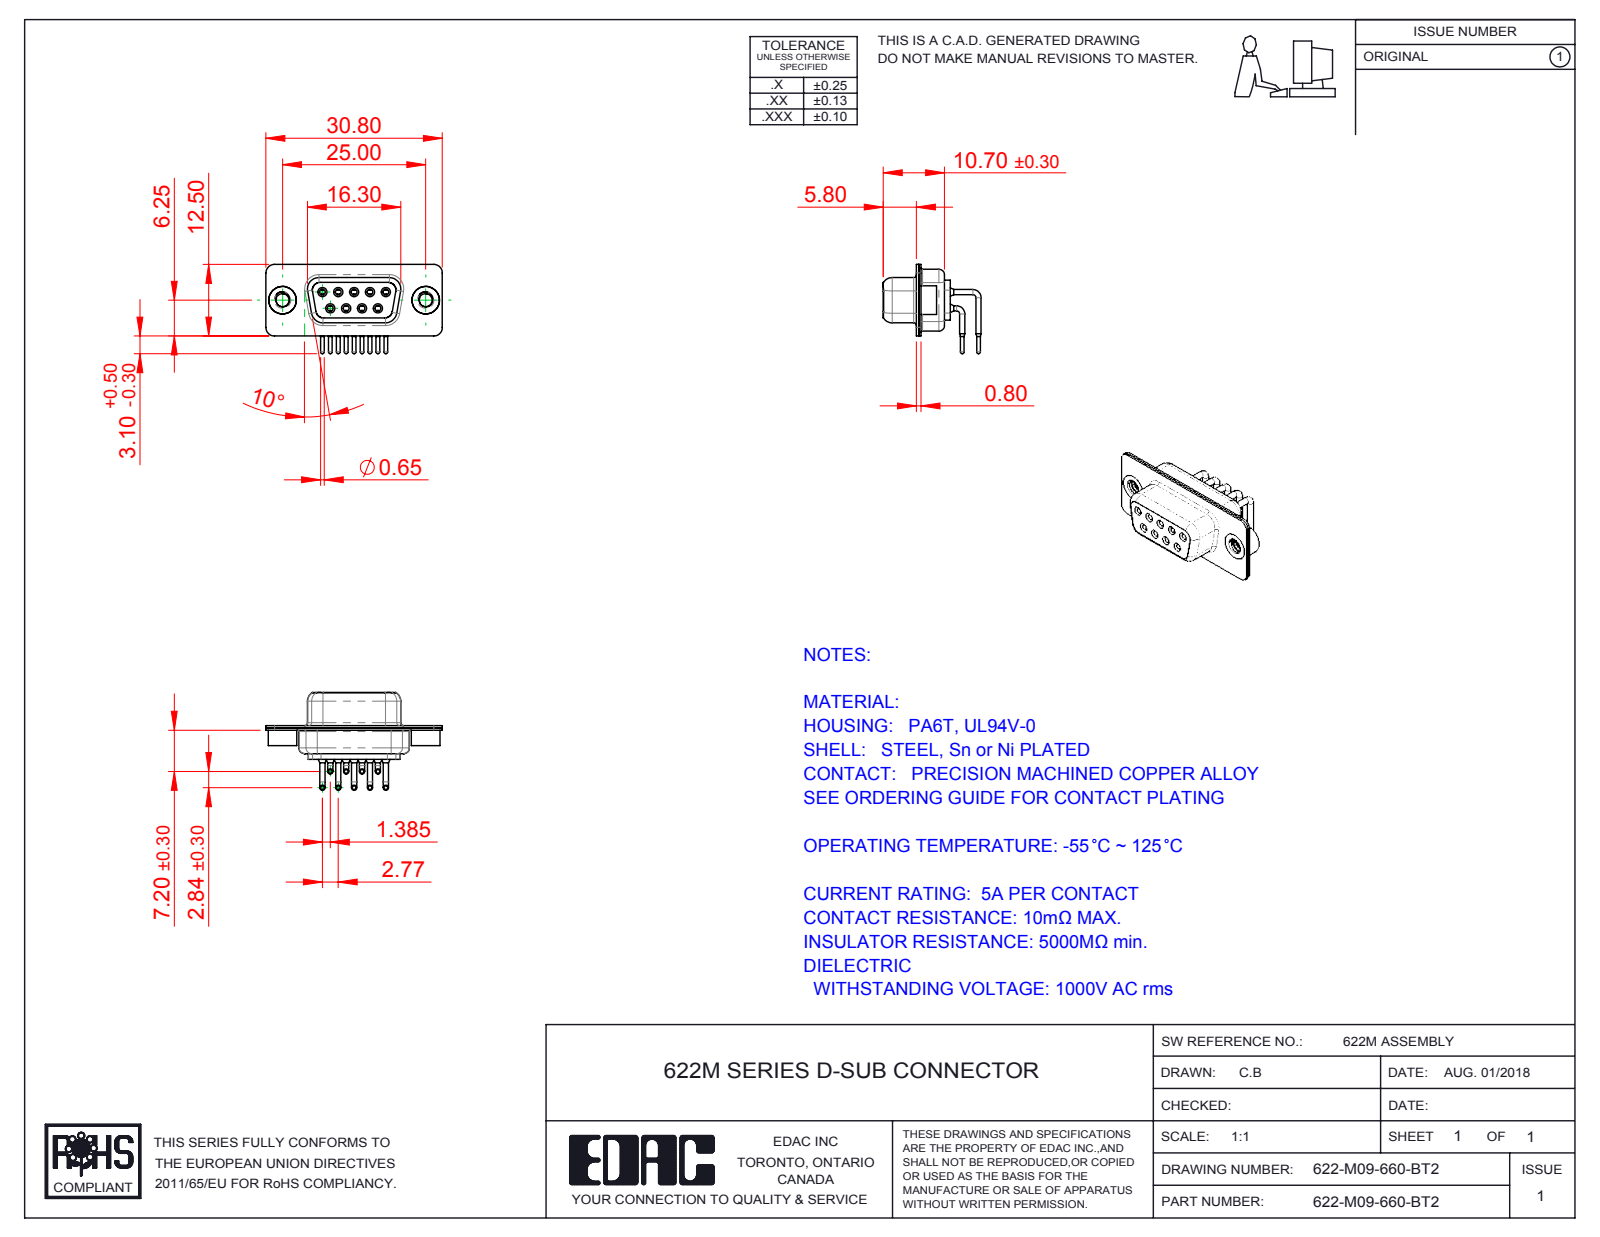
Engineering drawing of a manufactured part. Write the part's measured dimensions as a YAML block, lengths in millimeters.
part_name: "622M 4-40 Threaded Rivet; 622M Housing_09 Contacts; 622-M09-660-BT2; 622M Shell Front_09 Contacts (+3 more)"
step_written_by: "SolidWorks 2016 (CONFIG_CONTROL_DESIGN)"
units: millimeters
bodies: {solids: 14, faces: 756, planar: 202, cylindrical: 344, other: 210}
overall_size: [30.8, 17.09, 15.6]
volume: 1745
surface_area: 4559
round_holes:
  - {diameter: 1, count: 9}
  - {diameter: 1.1, count: 9}
  - {diameter: 1.7, count: 9}
  - {diameter: 1.8, count: 9}
  - {diameter: 2, count: 9}
  - {diameter: 2.26, count: 2}
  - {diameter: 4, count: 2}
  - {diameter: 4.8, count: 2}
round_bosses_or_shafts:
  - {diameter: 0.9, count: 18}
  - {diameter: 1.6, count: 9}
  - {diameter: 1.5, count: 9}
  - {diameter: 0.65, count: 9}
  - {diameter: 5, count: 2}
  - {diameter: 4.9, count: 2}
partial_cylinders:
  - {radius: 1.5, count: 16}
  - {radius: 2, count: 12}
  - {radius: 1.35, count: 8}
  - {radius: 1.6, count: 8}
  - {radius: 0.25, count: 4}
  - {radius: 0.5, count: 4}
  - {radius: 0.6, count: 4}
  - {radius: 0.65, count: 4}
face_to_face_distances: [0.4, 0.8, 1.45, 2.3, 8.95, 6.2, 8.5, 1.9, 0.85, 9.35]
hole_center_spacings: [3.16, 2.77, 5.54, 5.03, 5.04, 8.31, 7.1, 7.48]
